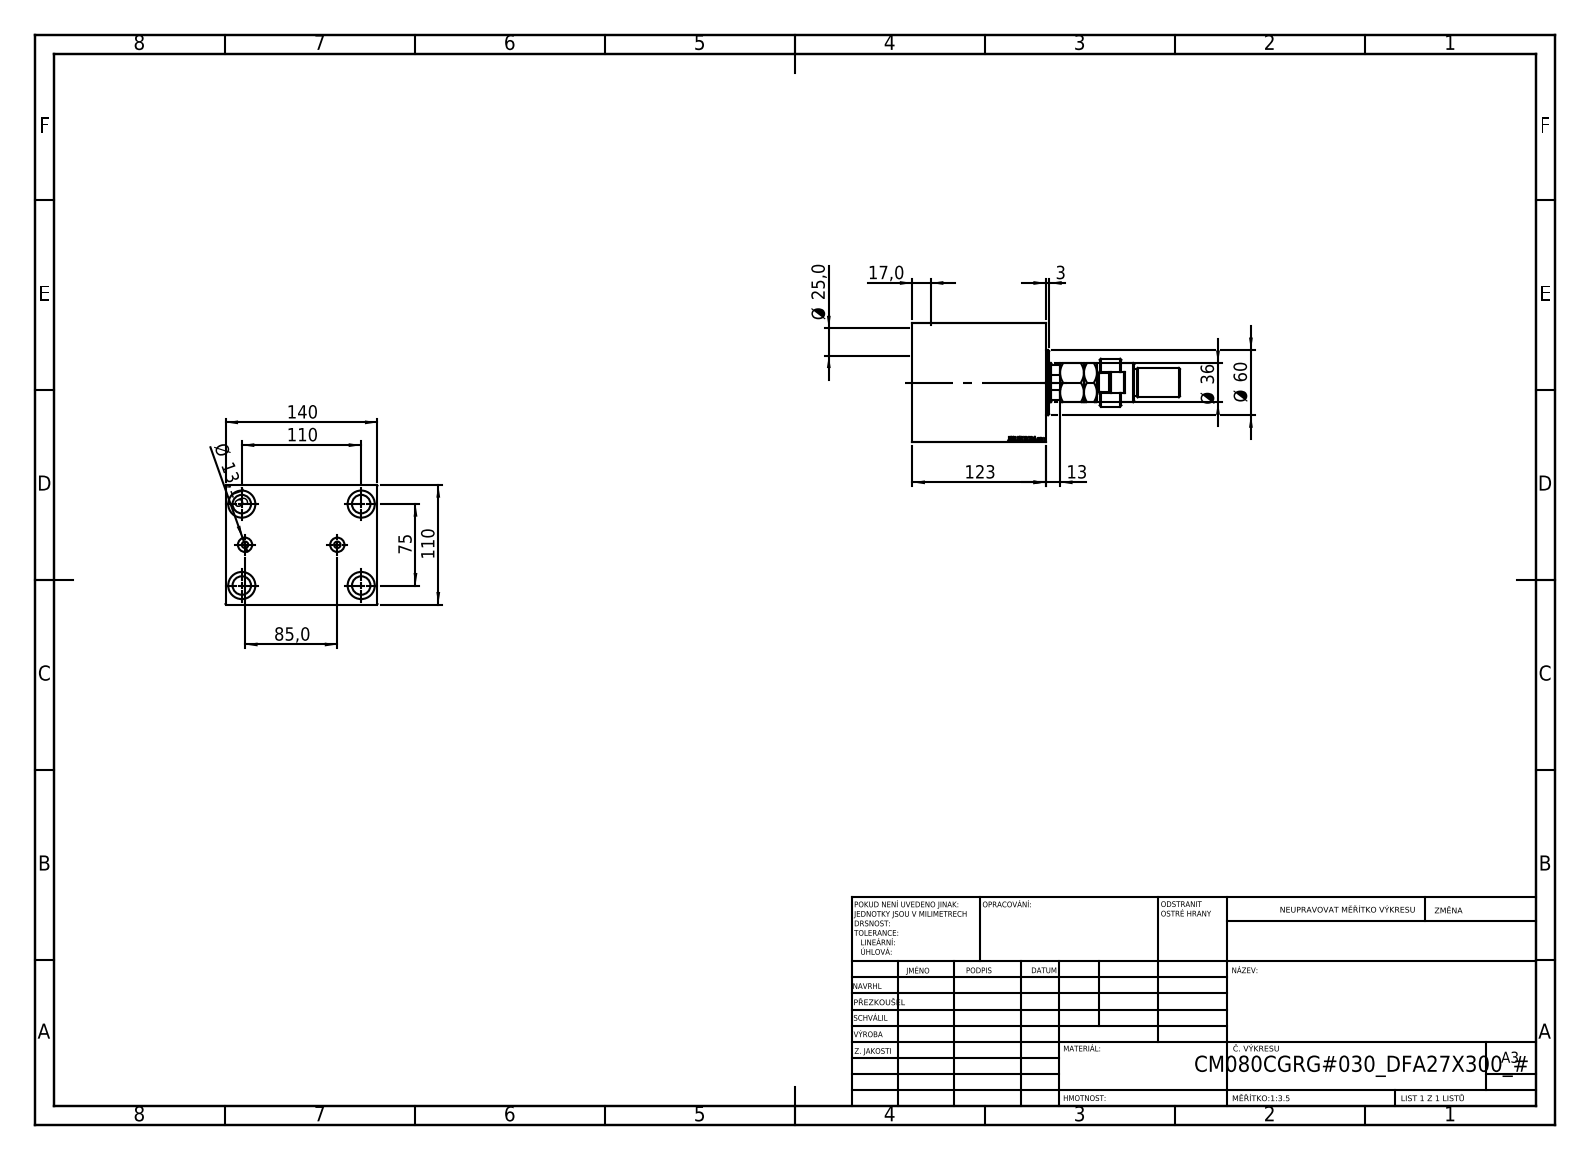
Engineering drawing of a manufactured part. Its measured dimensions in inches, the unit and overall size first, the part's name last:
Units: inches
Overall size (bounding box): 9.705 × 5.512 × 4.331
Round holes (diameter × count): ⌀0.669 ×4, ⌀0.984 ×4, ⌀0.236 ×2, ⌀0.518 ×2, ⌀1.004 ×1, ⌀1.555 ×1, ⌀3.15 ×1, ⌀3.228 ×1, ⌀3.425 ×1
Round bosses / shafts (diameter × count): ⌀2.362 ×1, ⌀1.732 ×1, ⌀1.417 ×1, ⌀1.102 ×1, ⌀1.063 ×1, ⌀0.984 ×1, ⌀0.709 ×1
Partial cylindrical surfaces — rounded edges, fillets, slot ends (radius × count): R0.374 ×1, R0.591 ×1, R0.689 ×1
Main face-to-face distances: 4.331, 5.512, 4.843, 2.835, 2.008, 0.394, 0.85, 1.157, 3.992, 3.598
Hole centre spacings: 2.621, 1.481, 1.712, 2.953, 3.766, 4.331, 4.464, 5.242
Volume: 109.7 in³ · Surface area: 309.1 in²
Bodies: 5 solids, 945 faces (436 planar, 71 cylindrical, 438 other)
Part name (STEP PRODUCT): MFA; V450CM_C_VCP; FEMALE_PART_FOR_DFA; V450CM_C_Body (+1 more)
STEP written by: SolidWorks 2019 (CONFIG_CONTROL_DESIGN)
